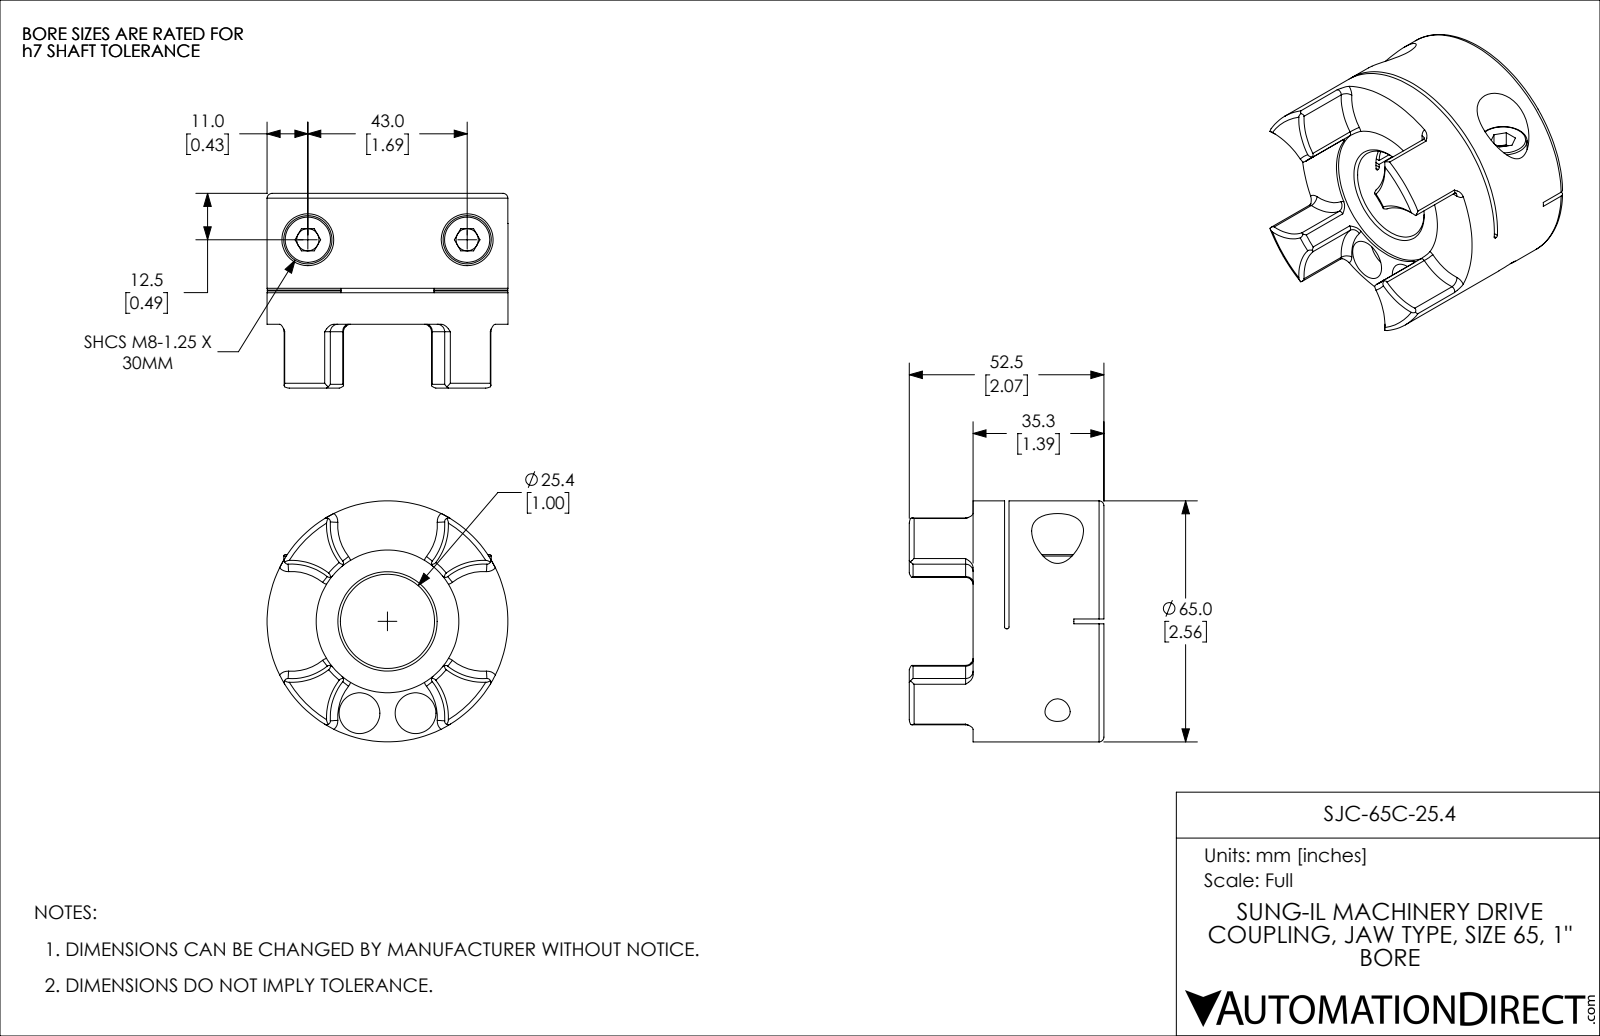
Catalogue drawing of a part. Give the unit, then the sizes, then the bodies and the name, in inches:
Units: inches
Overall size (bounding box): 2.559 × 2.559 × 2.067
Round holes (diameter × count): ⌀0.236 ×2, ⌀0.268 ×2, ⌀0.335 ×2, ⌀0.433 ×2, ⌀0.551 ×2, ⌀1 ×1, ⌀1.516 ×1
Round bosses / shafts (diameter × count): ⌀0.512 ×2, ⌀0.315 ×2, ⌀2.559 ×1
Partial cylindrical surfaces — rounded edges, fillets, slot ends (radius × count): R0.039 ×16, R0.608 ×4, R0.02 ×2, R1.969 ×1
Main face-to-face distances: 1.055, 0.047, 1.008, 0.335, 0.382, 1.39, 0.051, 0.031, 0.303, 0.35
Hole centre spacings: 1.019, 0.596, 1.693
Volume: 6.178 in³ · Surface area: 44.26 in²
Bodies: 3 solids, 216 faces (52 planar, 77 cylindrical, 87 other)
Part name (STEP PRODUCT): SJC-65C-25.4
STEP written by: SolidWorks 2021 (CONFIG_CONTROL_DESIGN)
